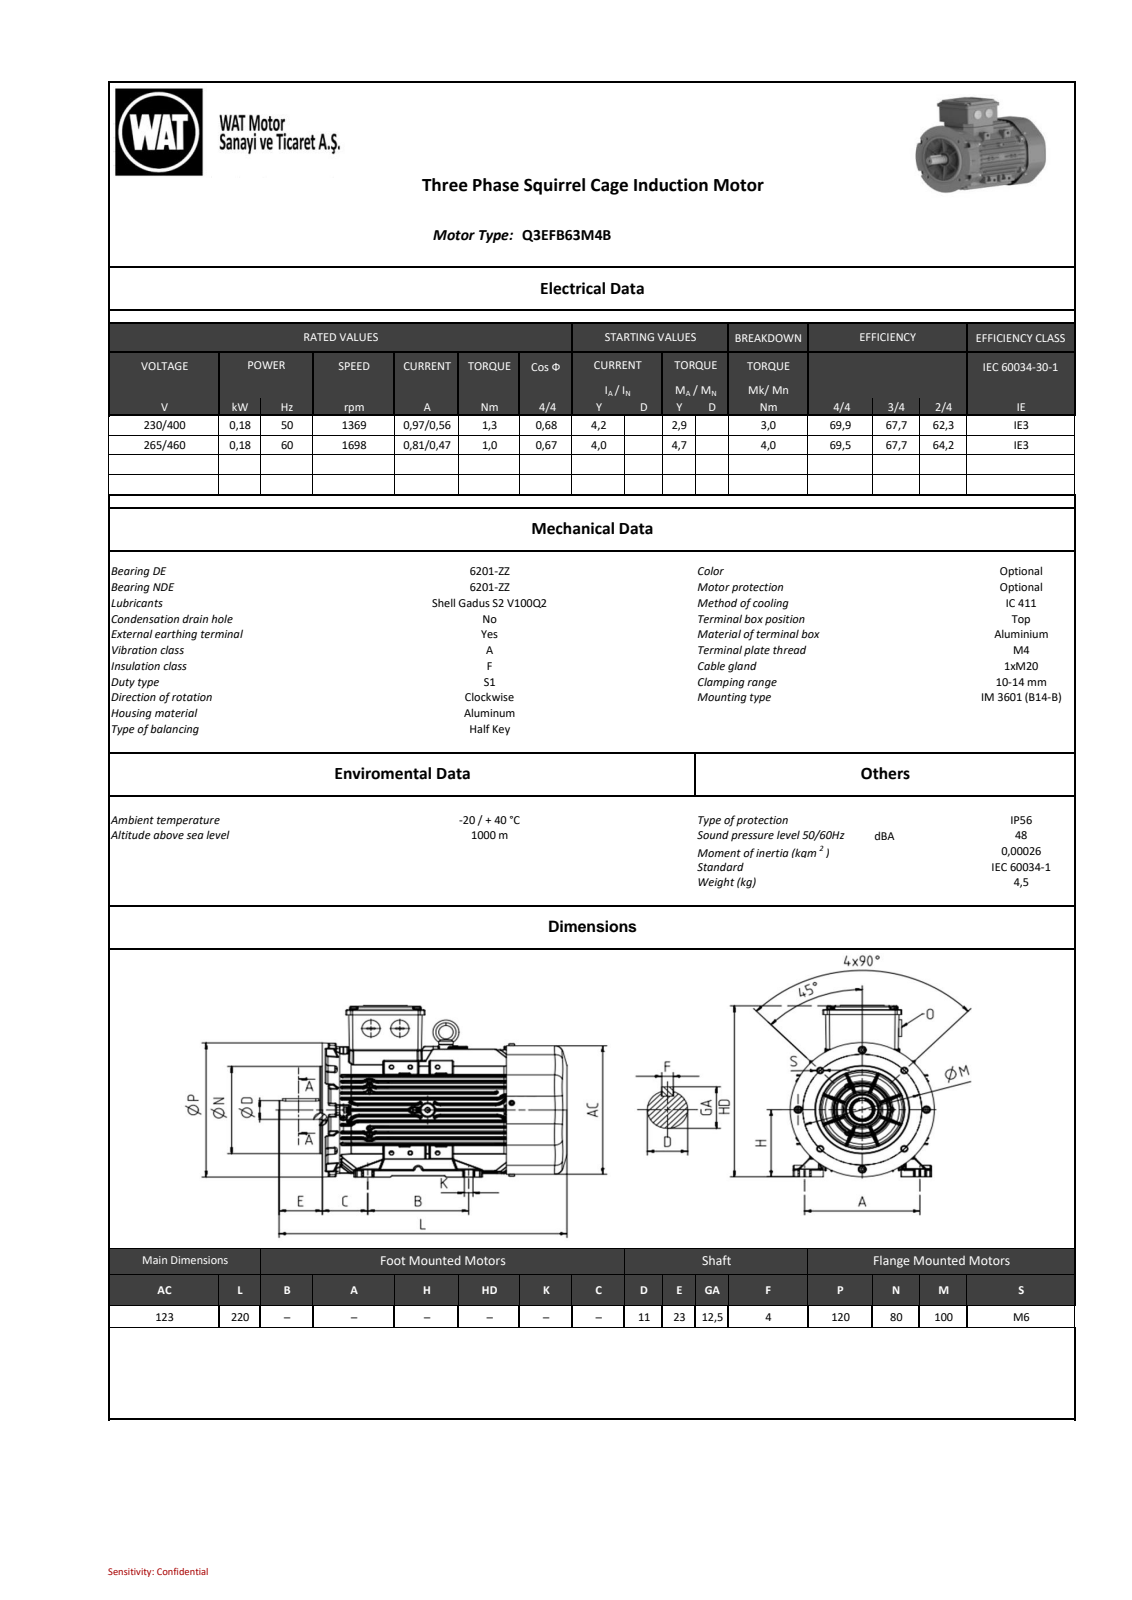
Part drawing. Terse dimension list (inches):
name: QE series_ 63_B14b_stp_objects
written by: SIEMENS PLM Software NX2206.8101 (AP203_CONFIGURATION_CONTROLLED_3D_DESIGN_OF_MECHANICAL_PARTS_AND_ASSEMBLIES_MIM_LF)
unit: in
bodies: 0 solids, 1415 faces (747 planar, 410 cylindrical, 258 other)
size: 8.642 × 6.283 × 5.039
holes: 8× ⌀0.144, 4× ⌀0.098, 4× ⌀0.236, 2× ⌀0.118, 1× ⌀0.315, 1× ⌀0.441, 1× ⌀0.571, 1× ⌀2.835, 1× ⌀4.764
bosses: 8× ⌀0.315, 4× ⌀0.157, 1× ⌀4.843, 1× ⌀4.724, 1× ⌀3.15, 1× ⌀1.024, 1× ⌀0.748
rounds: 111× R0.02, 37× R0.039, 37× R0.079, 28× R0.059, 14× R0.004, 12× R0.053, 8× R0.157, 6× R0.012
face distances: 1.101, 0.55, 0.557, 0.273, 0.271, 0.828, 0.276, 0.278, 0.823, 1.38
hole spacings: 1.969, 2.126, 2.48, 2.784, 3.267, 0.394, 0.197, 1.24
